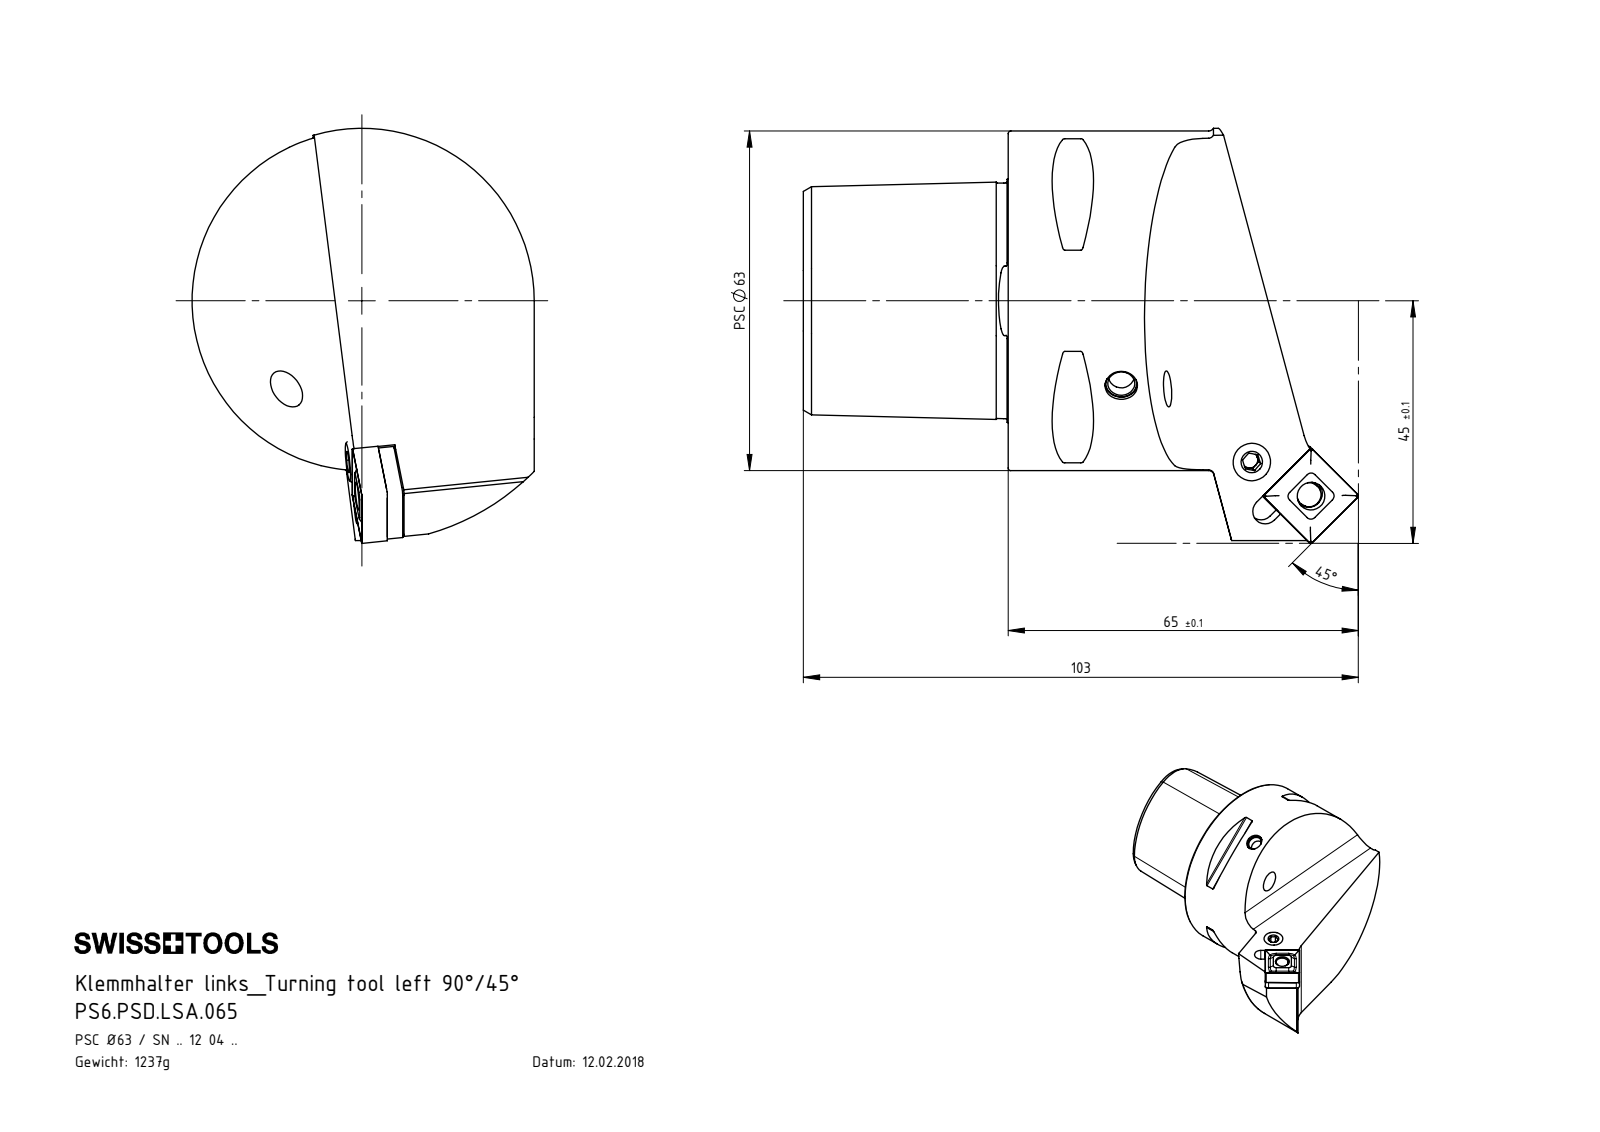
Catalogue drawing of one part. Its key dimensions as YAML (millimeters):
part_name: "KVT_MB_600_060; WSD-ER2.101.003_A; PS6.PSD.LSA.065; WCD-ER4.101.017_A (+4 more)"
step_written_by: "SolidWorks 2017 (AUTOMOTIVE_DESIGN)"
units: millimeters
bodies: {solids: 8, faces: 338, planar: 90, cylindrical: 83, other: 165}
overall_size: [103, 77, 63.5]
volume: 157115
surface_area: 30313
round_holes:
  - {diameter: 5, count: 2}
  - {diameter: 4, count: 1}
  - {diameter: 5.16, count: 1}
  - {diameter: 6.4, count: 1}
  - {diameter: 7, count: 1}
  - {diameter: 8.1, count: 1}
  - {diameter: 8.4, count: 1}
  - {diameter: 18, count: 1}
  - {diameter: 28, count: 1}
  - {diameter: 32, count: 1}
round_bosses_or_shafts:
  - {diameter: 63, count: 1}
  - {diameter: 8, count: 1}
  - {diameter: 7.9, count: 1}
  - {diameter: 6.4, count: 1}
  - {diameter: 6, count: 1}
  - {diameter: 4.5, count: 1}
  - {diameter: 3.55, count: 1}
partial_cylinders:
  - {radius: 0.5, count: 8}
  - {radius: 0.4, count: 4}
  - {radius: 1.2, count: 4}
  - {radius: 2.5, count: 2}
  - {radius: 6, count: 2}
  - {radius: 2.2, count: 1}
  - {radius: 2.35, count: 1}
  - {radius: 2.8, count: 1}
face_to_face_distances: [38, 24.88, 4.45, 27, 11, 3.18, 7.63, 55.8, 12.19, 12.7]
hole_center_spacings: [12.8, 12.81, 27.5]
